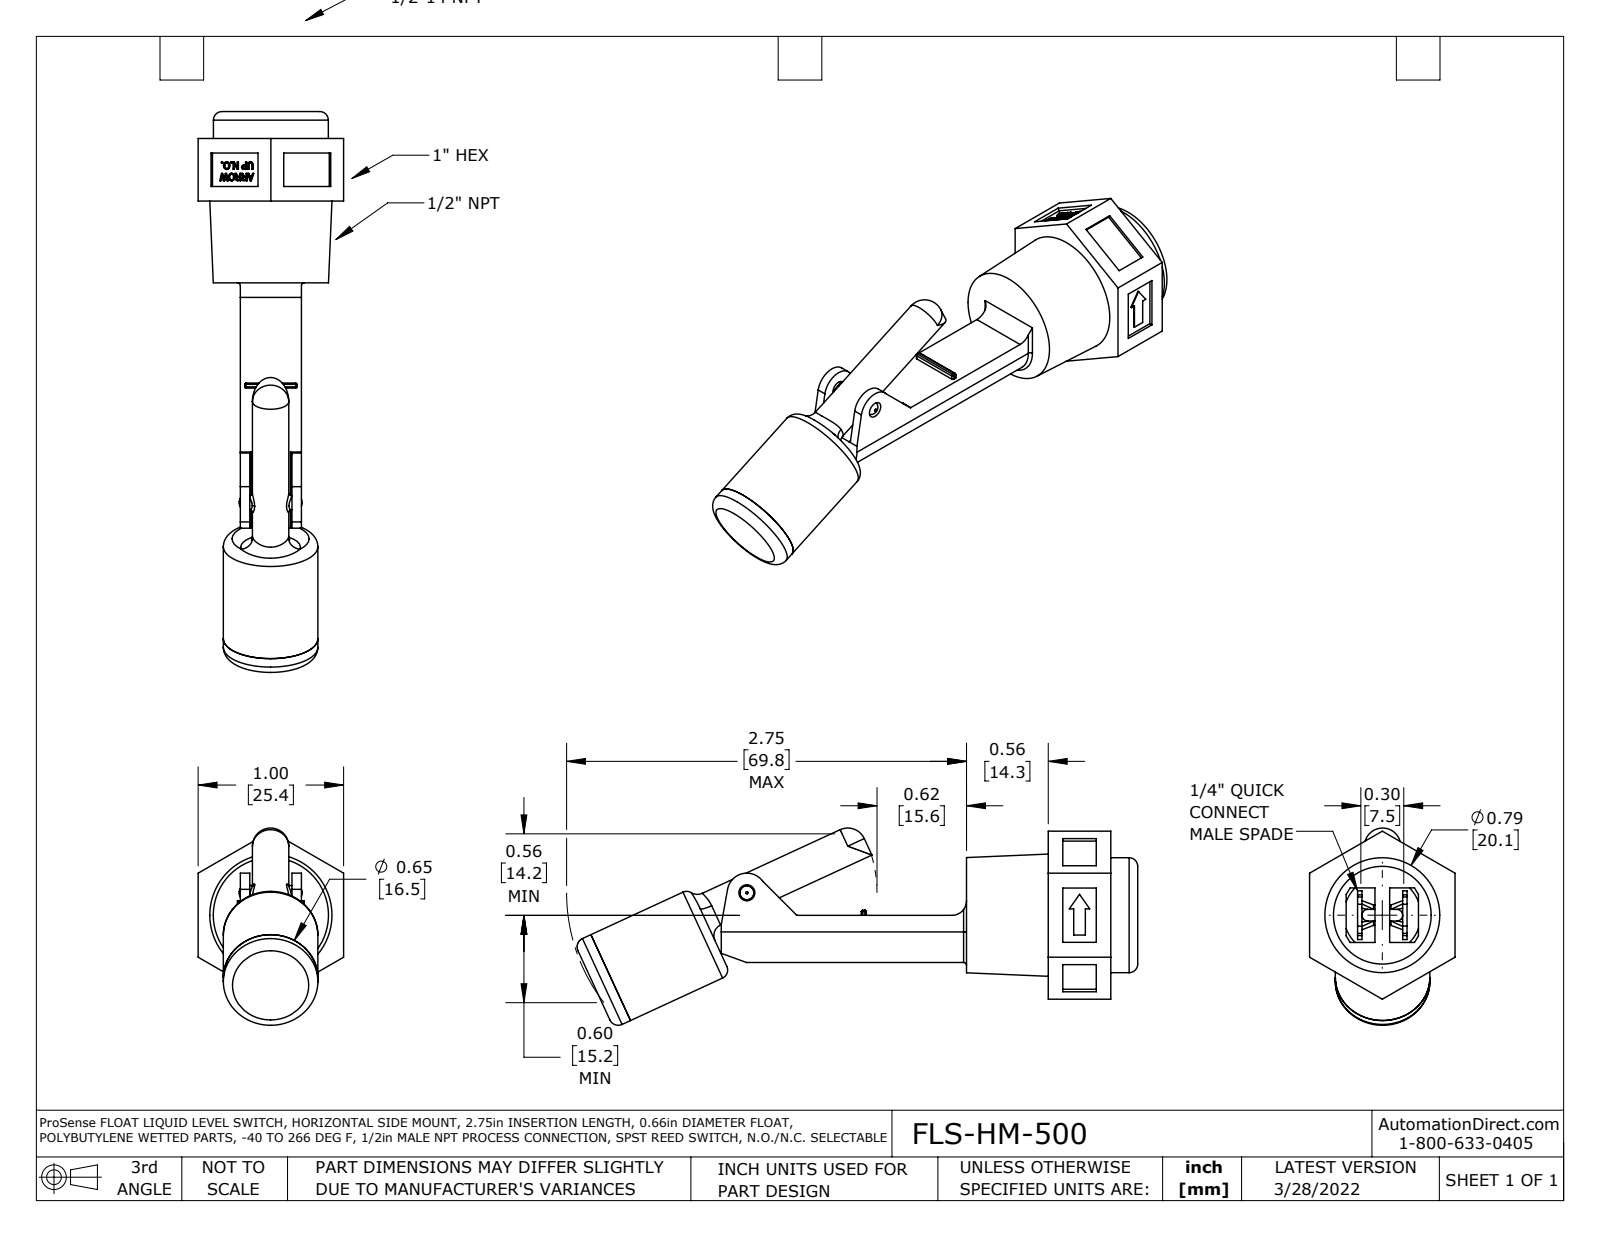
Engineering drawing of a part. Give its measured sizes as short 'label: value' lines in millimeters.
name: FLS-HM-500
written by: SolidWorks 2021 (AUTOMOTIVE_DESIGN)
unit: mm
bodies: 6 solids, 582 faces (367 planar, 60 cylindrical, 155 other)
size: 97.9 × 34.4 × 25.4
volume: 14 800 mm³; area: 11 630 mm²
holes: 2× ⌀13.5, 1× ⌀1.9, 1× ⌀1.9, 1× ⌀2.8, 1× ⌀11.4, 1× ⌀12.7, 1× ⌀14.2
bosses: 2× ⌀16.5, 1× ⌀20.1, 1× ⌀14, 1× ⌀6.4, 1× ⌀3.2
rounds: 9× R0.3, 4× R0.2, 2× R0.5, 2× R1, 2× R1.8, 1× R2.5, 1× R3.2, 1× R3.4
face distances: 25.4, 0.5, 24.9, 4.7, 8.4, 7.4, 18, 0.8, 10.9, 25.2
hole spacings: 62.9
